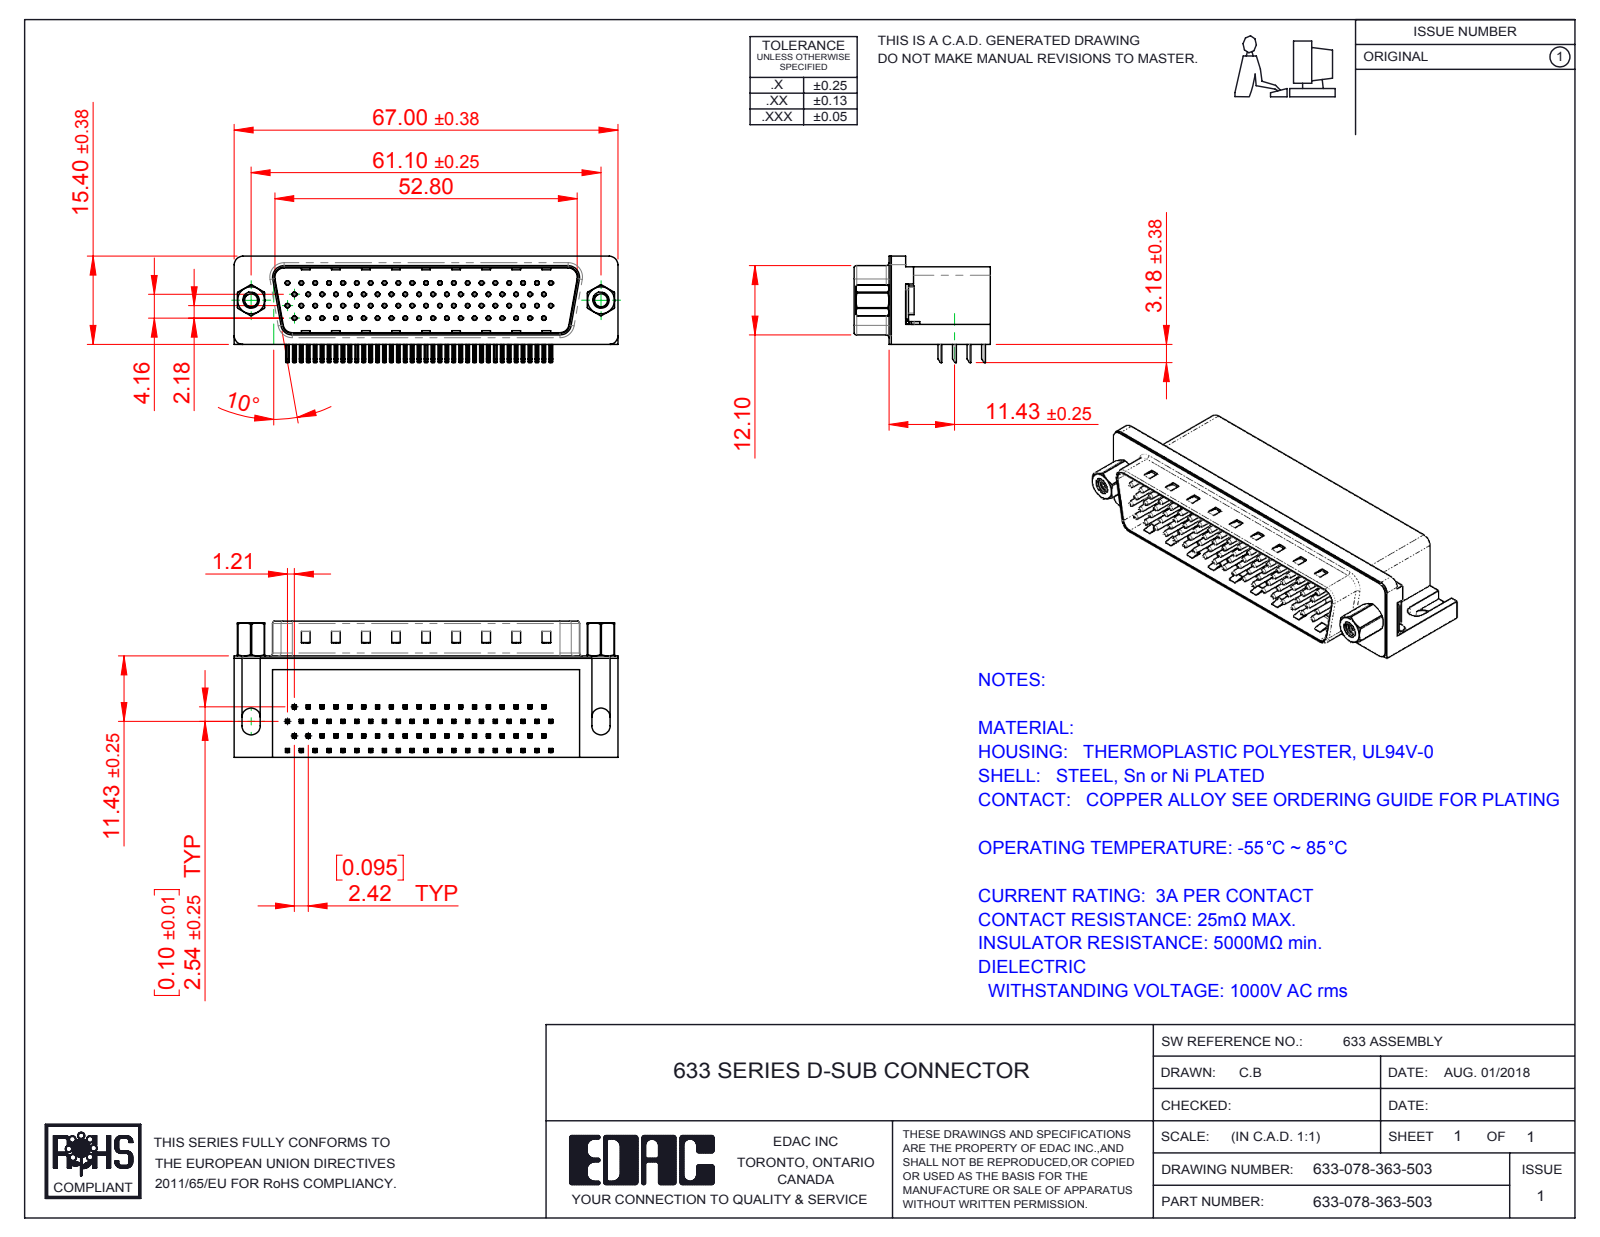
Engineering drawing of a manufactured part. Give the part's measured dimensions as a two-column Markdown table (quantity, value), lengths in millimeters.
| quantity | value |
| --- | --- |
| part name | 633 4-40 Hex Standoff; 633 Housing_78 Contact; 633 Shell_78 Contact; 633 Contact Bottom_78 Contact (+6 more) |
| STEP written by | SolidWorks 2016 (CONFIG_CONTROL_DESIGN) |
| units | millimeters |
| bodies | 86 solids, 6390 faces (4001 planar, 1838 cylindrical, 551 other) |
| overall size | 67 × 23.8 × 18.58 |
| volume | 14 767 mm³ |
| surface area | 16 578 mm² |
| round holes (diameter × count) | 0.35 × 78, 0.8 × 78, 2.26 × 2, 2.29 × 2, 4 × 2, 4.8 × 2, 5 × 2 |
| round bosses / shafts (diameter × count) | 0.75 × 78, 4.9 × 2, 4.75 × 2, 3.9 × 2, 2.79 × 2 |
| partial cylindrical surfaces (radius × count) | 0.25 × 320, 0.12 × 156, 1 × 16, 0.5 × 9, 1.6 × 8, 1.5 × 6, 0.45 × 4, 0.9 × 4 |
| main face-to-face distances | 0.4, 13.2, 17.3, 11.7, 13.35, 2.05, 13.75, 1.65, 11.9, 1.85 |
| hole center spacings | 2.42, 4.84, 7.26, 9.68, 6.26, 7.13, 12.1, 8.62 |
